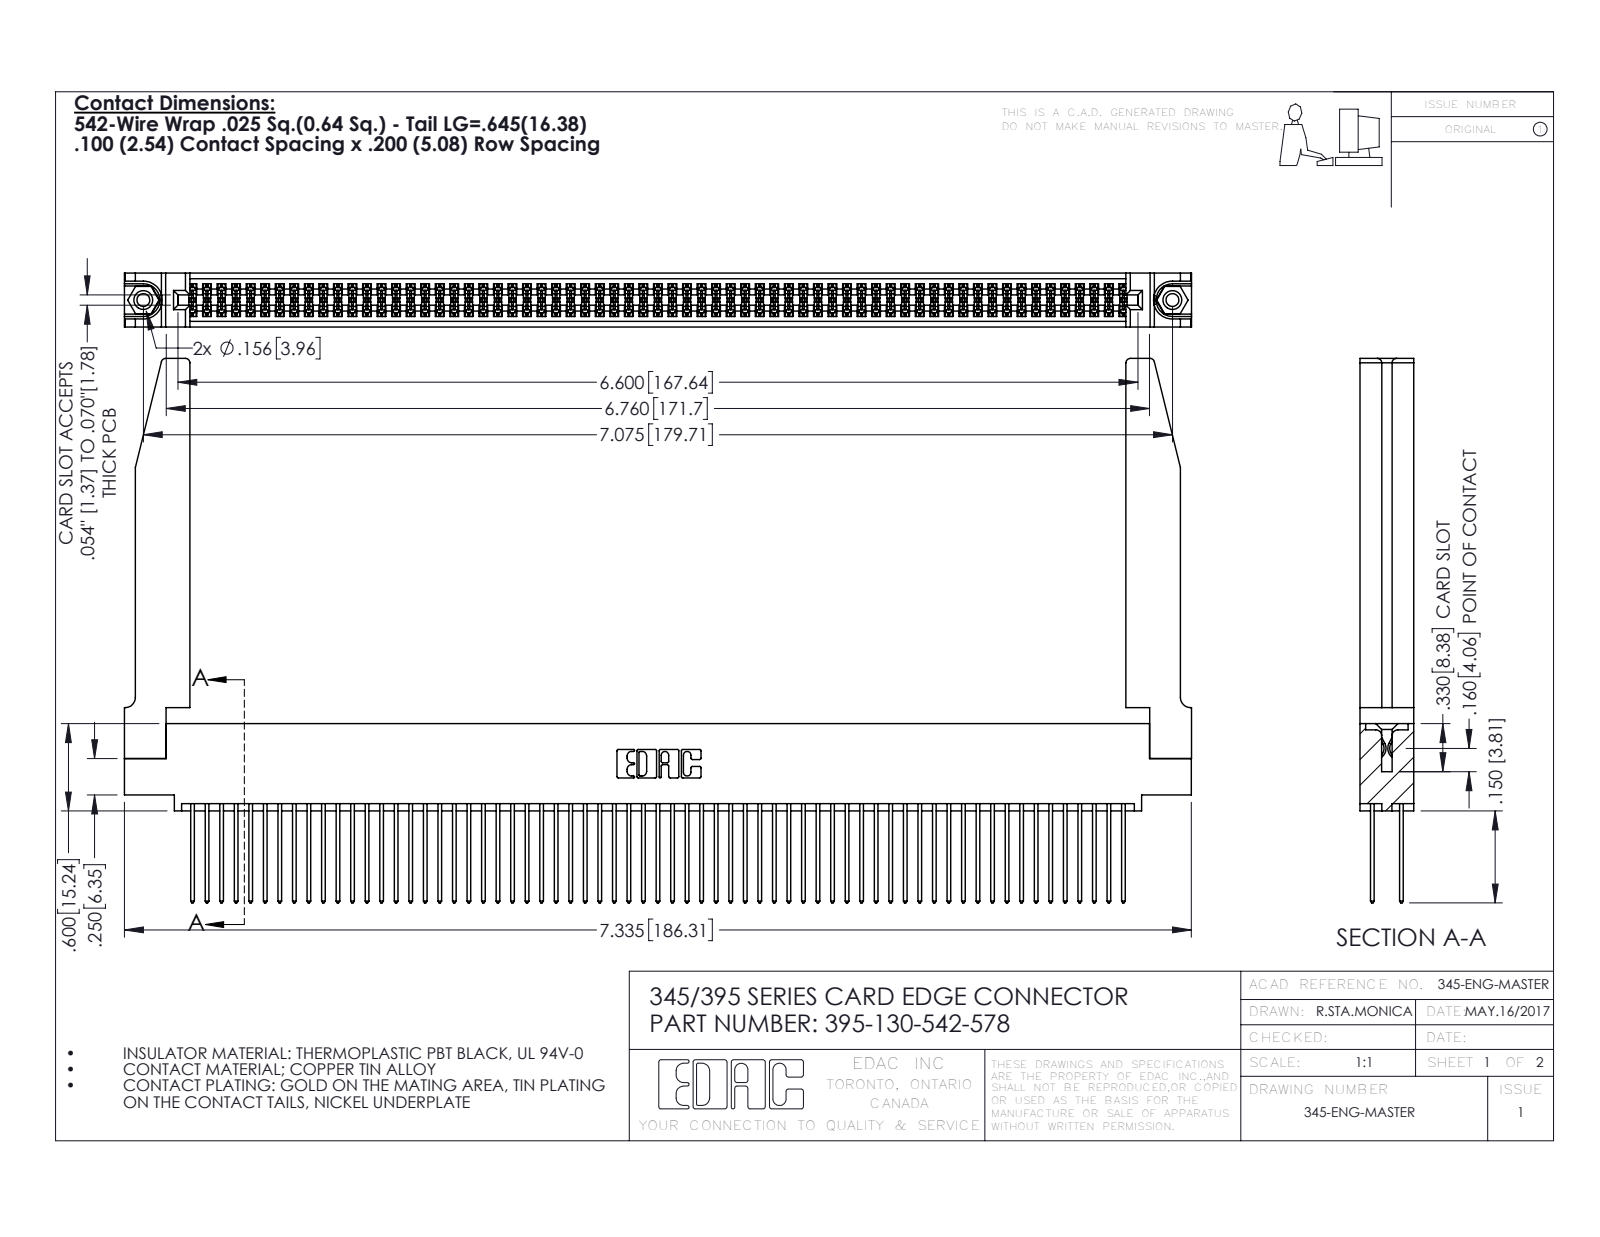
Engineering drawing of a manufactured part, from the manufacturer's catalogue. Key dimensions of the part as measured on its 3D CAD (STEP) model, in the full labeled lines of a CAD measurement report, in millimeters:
Part name (STEP PRODUCT): 345-250-001_345-250-001-102; 395-130-542-578; 345-292-001_345-293-142; 345 Part_0.110 Offset - 0.156 Dia-TH (+1 more)
STEP written by: SolidWorks 2016 (CONFIG_CONTROL_DESIGN)
Units: millimetres
Bodies: 135 solids, 6864 faces (4516 planar, 2296 cylindrical, 52 other)
Overall size (bounding box): 186.3 × 95 × 9.4
Volume: 26 610 mm³ · Surface area: 38 060 mm²
Round holes (diameter × count): ⌀2.3 ×2, ⌀3.2 ×2, ⌀4 ×2, ⌀1.6 ×1
Round bosses / shafts (diameter × count): ⌀3.9 ×2
Partial cylindrical surfaces — rounded edges, fillets, slot ends (radius × count): R0.2 ×195, R0.3 ×130, R0.3 ×22, R0.8 ×8, R0.2 ×6, R0.8 ×6, R0.7 ×3, R0.4 ×2
Main face-to-face distances: 1.8, 7.6, 9.4, 5.1, 2.5, 6.9, 0.6, 5.7, 4.4, 3.8
Hole centre spacings: 6.9, 173.7, 179.7
